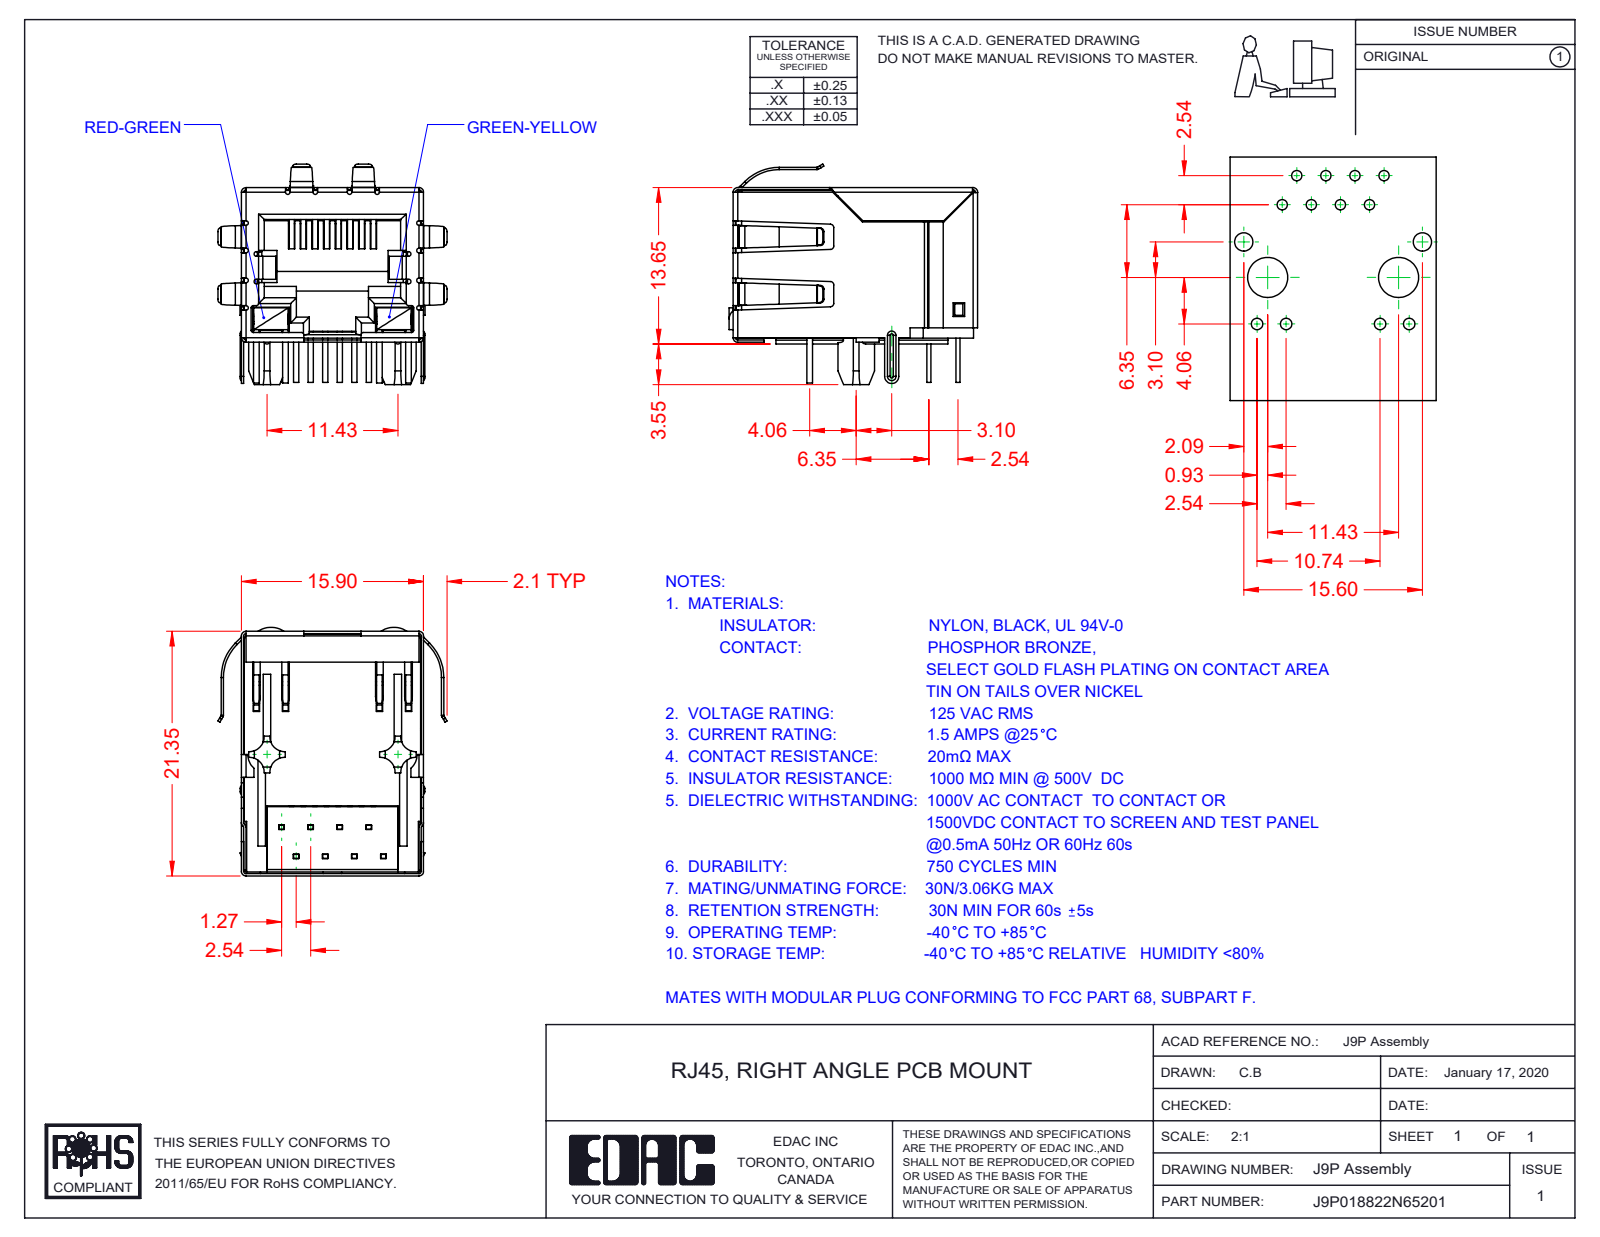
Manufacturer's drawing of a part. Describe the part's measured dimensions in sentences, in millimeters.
The part is named "9P-LED Insulator; J9P018822N65202; 9P-LED Shield; 9P-LED LED RH_5-Green-Yellow (+4 more)". Its 3-D file was written by "SolidWorks 2016 (CONFIG_CONTROL_DESIGN)". It is 13 solids with 1476 faces: 1042 planar, 340 cylindrical and 94 other. Overall it measures 21.7 by 20 by 19.25 millimeters. Its volume is 2 687 cubic millimeters and its surface area 7 515 square millimeters. Partial cylindrical surfaces (rounded edges, fillets, slot ends): 39 of radius 0.2, 22 of radius 0.5, 20 of radius 0.3, 16 of radius 0.4, 8 of radius 1.3, 5 of radius 0.23, 4 of radius 0.11, 4 of radius 0.31. The main face-to-face distances are 15.45, 15.7, 15.65, 0.35, 0.54, 15.5, 12.36, 0.6, 1.4, 0.59.
